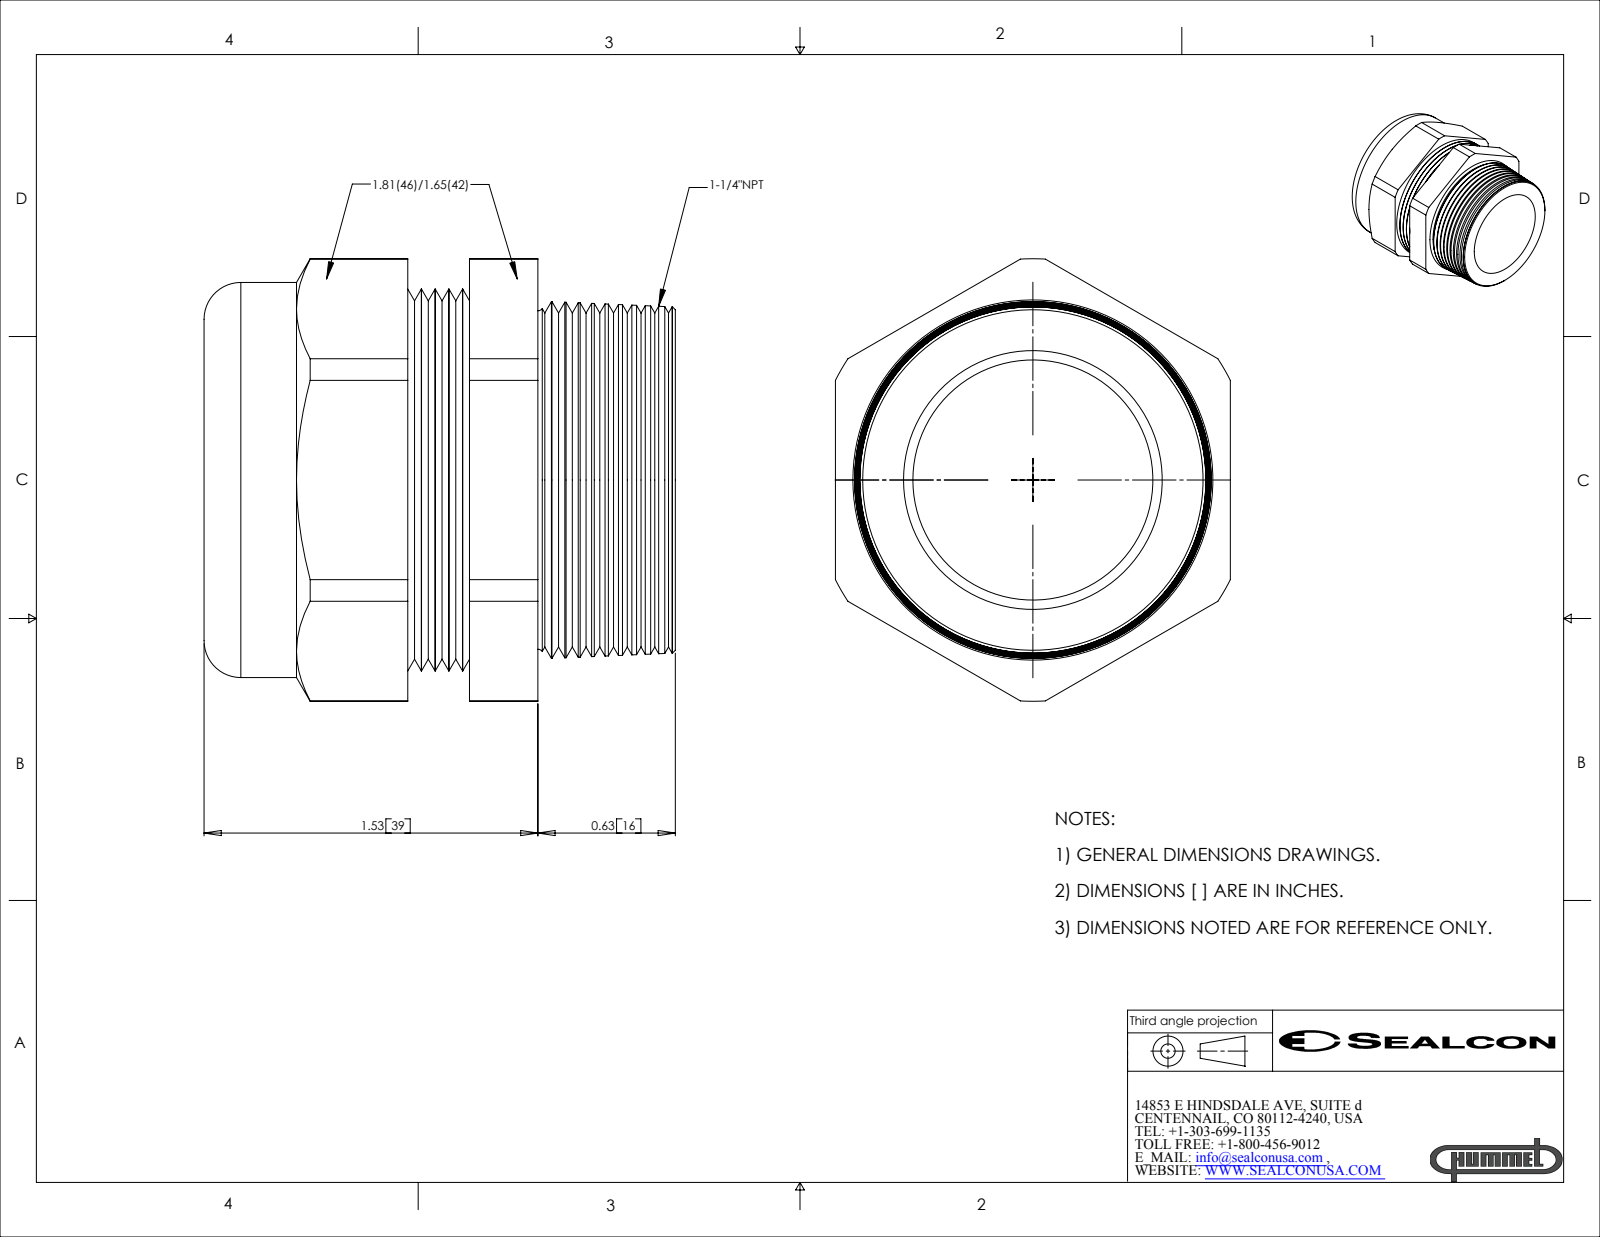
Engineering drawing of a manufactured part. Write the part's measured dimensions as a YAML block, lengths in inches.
part_name: "CD29LA-BK"
step_written_by: "SolidWorks 2007 (CONFIG_CONTROL_DESIGN)"
units: inches
bodies: {solids: 2, faces: 150, planar: 20, cylindrical: 32, other: 98}
overall_size: [2.16, 2.027, 1.81]
volume: 3.084
surface_area: 32.8
round_holes:
  - {diameter: 1.1, count: 1}
  - {diameter: 1.394, count: 1}
round_bosses_or_shafts:
  - {diameter: 1.81, count: 1}
  - {diameter: 1.749, count: 1}
partial_cylinders:
  - {radius: 1.014, count: 1}
face_to_face_distances: [1.81, 1.736, 1.106, 0.63, 0.404, 1.51, 2.14, 1.196, 0.793, 0.313]
